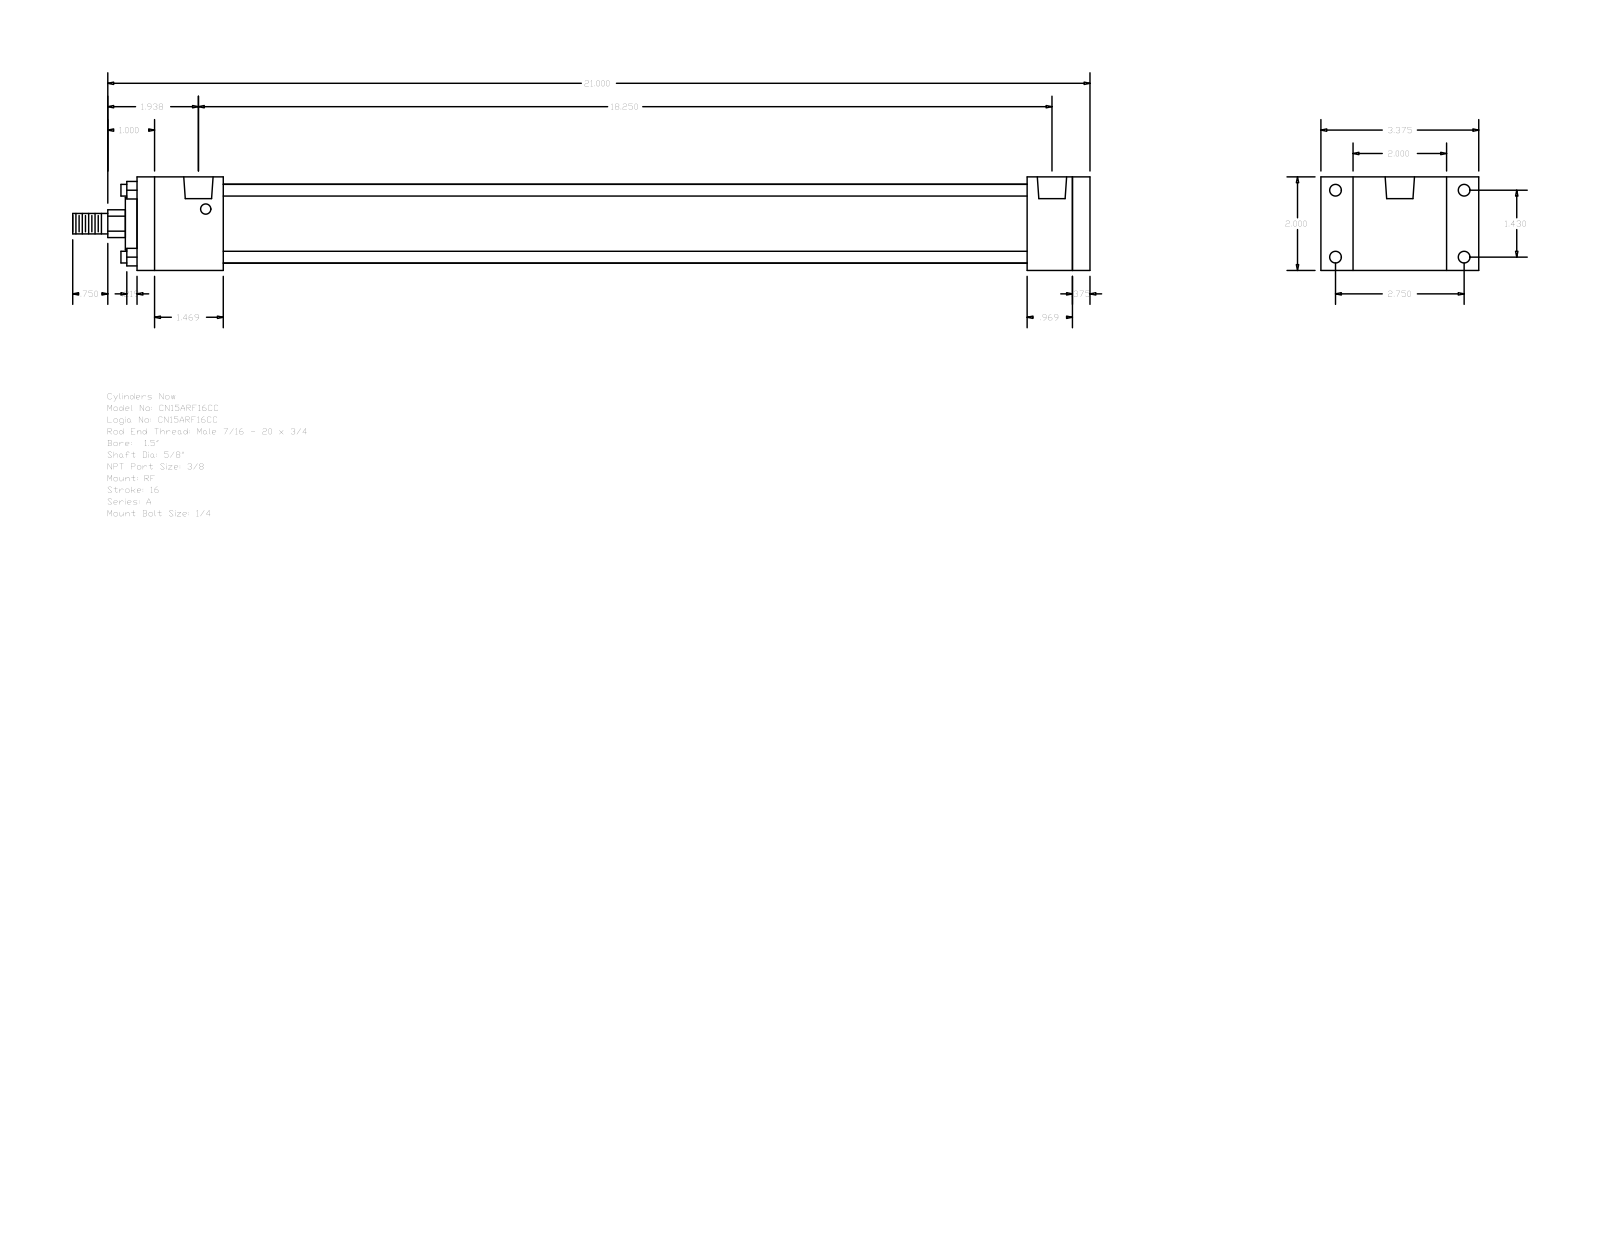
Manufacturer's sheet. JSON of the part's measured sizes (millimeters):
{"part_name": "A_RF__0150_0.625", "step_written_by": "GSSL Pune (CONFIG_CONTROL_DESIGN)", "units": "millimeters", "bodies": {"solids": 0, "faces": 92, "planar": 64, "cylindrical": 28, "other": 0}, "overall_size": [552.45, 85.72, 50.8], "round_holes": [[5.56, 4], [6.35, 4], [15.93, 2]], "round_bosses_or_shafts": [[6.35, 4], [42.93, 1], [28.57, 1], [15.88, 1], [11.11, 1]], "partial_cylinders_radius": [[7.54, 1]], "face_to_face_distances": [50.8, 9.52, 508, 517.52, 483.39, 24.61, 34.13, 46.83, 436.56, 461.17], "hole_center_spacings": [3.97, 36.32, 69.84, 78.72, 455.61, 459.58, 463.55]}
